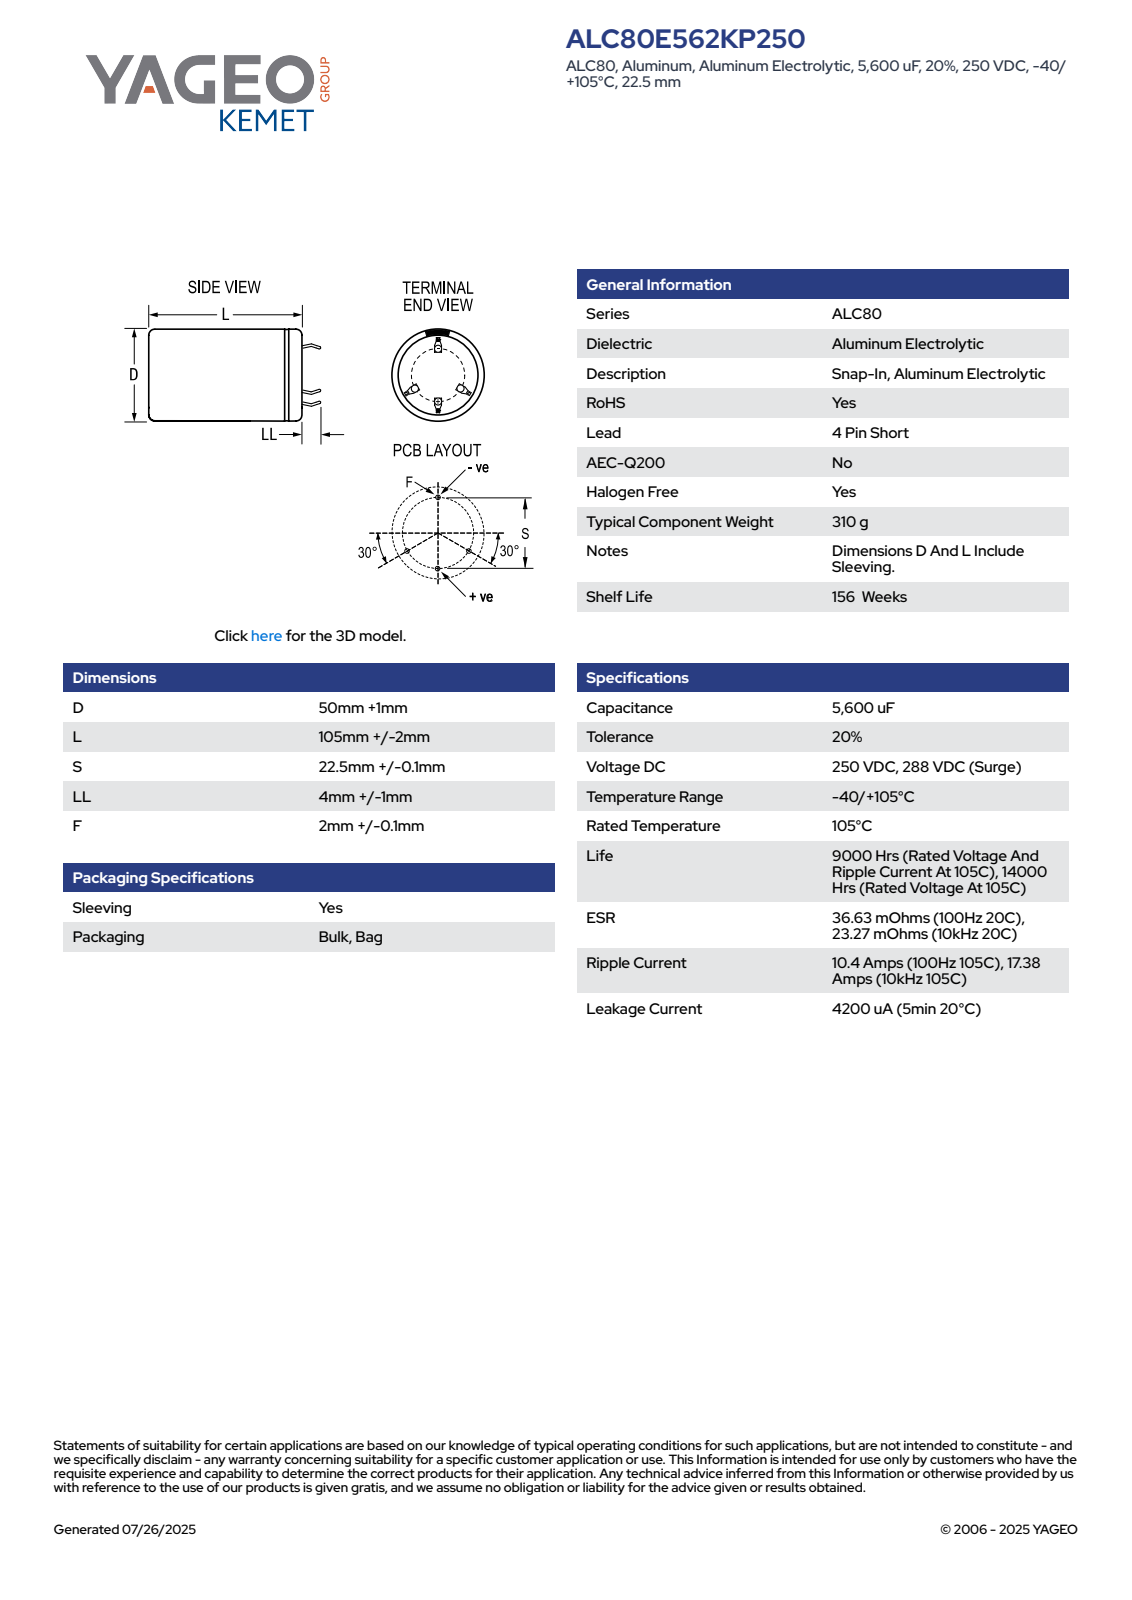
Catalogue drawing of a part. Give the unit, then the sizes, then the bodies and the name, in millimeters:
Units: millimetres
Overall size (bounding box): 111.99 × 51 × 51
Round holes (diameter × count): ⌀45.12 ×1
Round bosses / shafts (diameter × count): ⌀51 ×1
Partial cylindrical surfaces — rounded edges, fillets, slot ends (radius × count): R25.49 ×1
Main face-to-face distances: 106.99, 107.49, 0.5, 0.6, 0.75, 1.35, 11.96, 12.18, 12.39, 12.17
Volume: 217 073 mm³ · Surface area: 21 239 mm²
Bodies: 1 solid, 134 faces (80 planar, 15 cylindrical, 39 other)
Part name (STEP PRODUCT): CARS_K4P_50X105_D51L107S22.5LL5F2.1
STEP written by: SolidWorks 2014 (AUTOMOTIVE_DESIGN)
